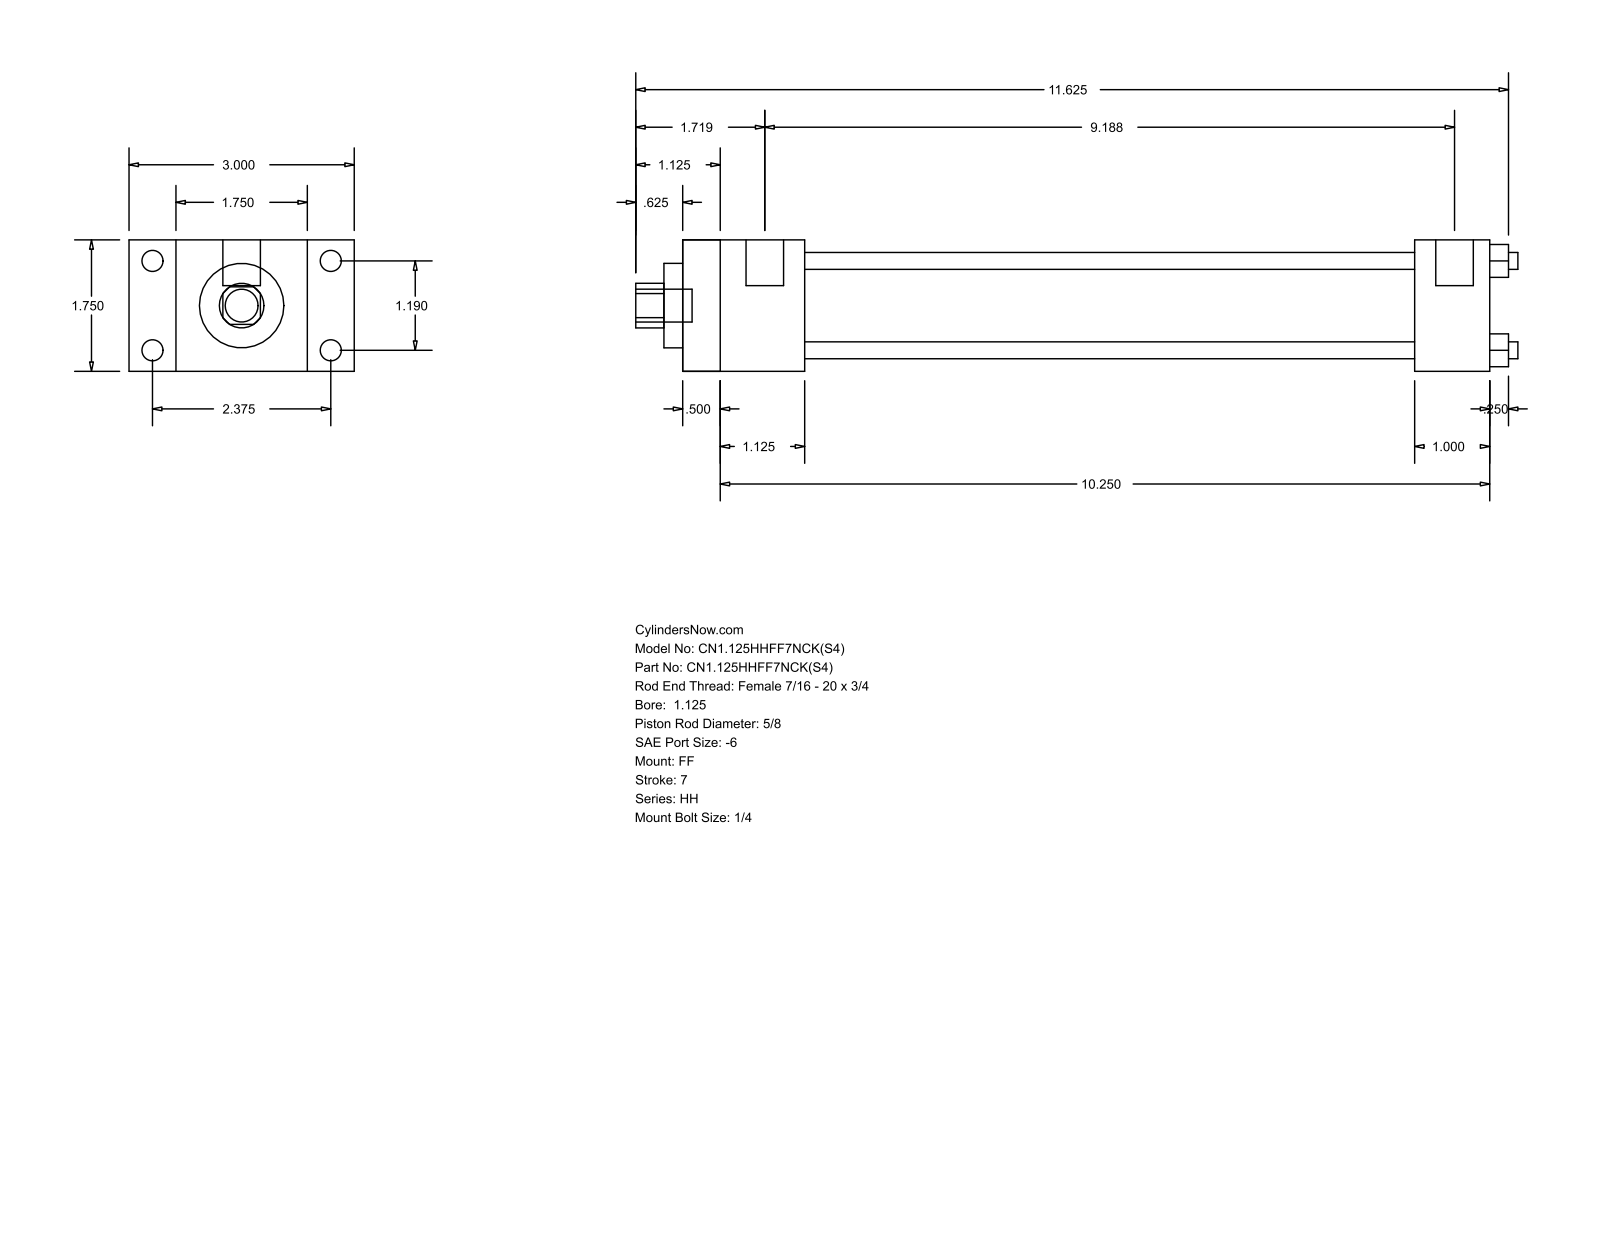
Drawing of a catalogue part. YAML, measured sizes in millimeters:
part_name: "HH_FF__0112_0.625"
step_written_by: "GSSL Pune (CONFIG_CONTROL_DESIGN)"
units: millimeters
bodies: {solids: 0, faces: 92, planar: 64, cylindrical: 28, other: 0}
overall_size: [298.45, 76.2, 44.45]
round_holes:
  - {diameter: 5.71, count: 4}
  - {diameter: 15.88, count: 1}
  - {diameter: 28.57, count: 1}
  - {diameter: 34.92, count: 1}
round_bosses_or_shafts:
  - {diameter: 7.14, count: 4}
  - {diameter: 5.56, count: 4}
  - {diameter: 12.7, count: 2}
  - {diameter: 11.11, count: 1}
partial_cylinders:
  - {radius: 7.54, count: 1}
face_to_face_distances: [44.46, 273.05, 15.87, 12.69, 260.36, 60.33, 28.58, 41.27, 247.64, 234.95]
hole_center_spacings: [21.37, 30.22, 42.74]
